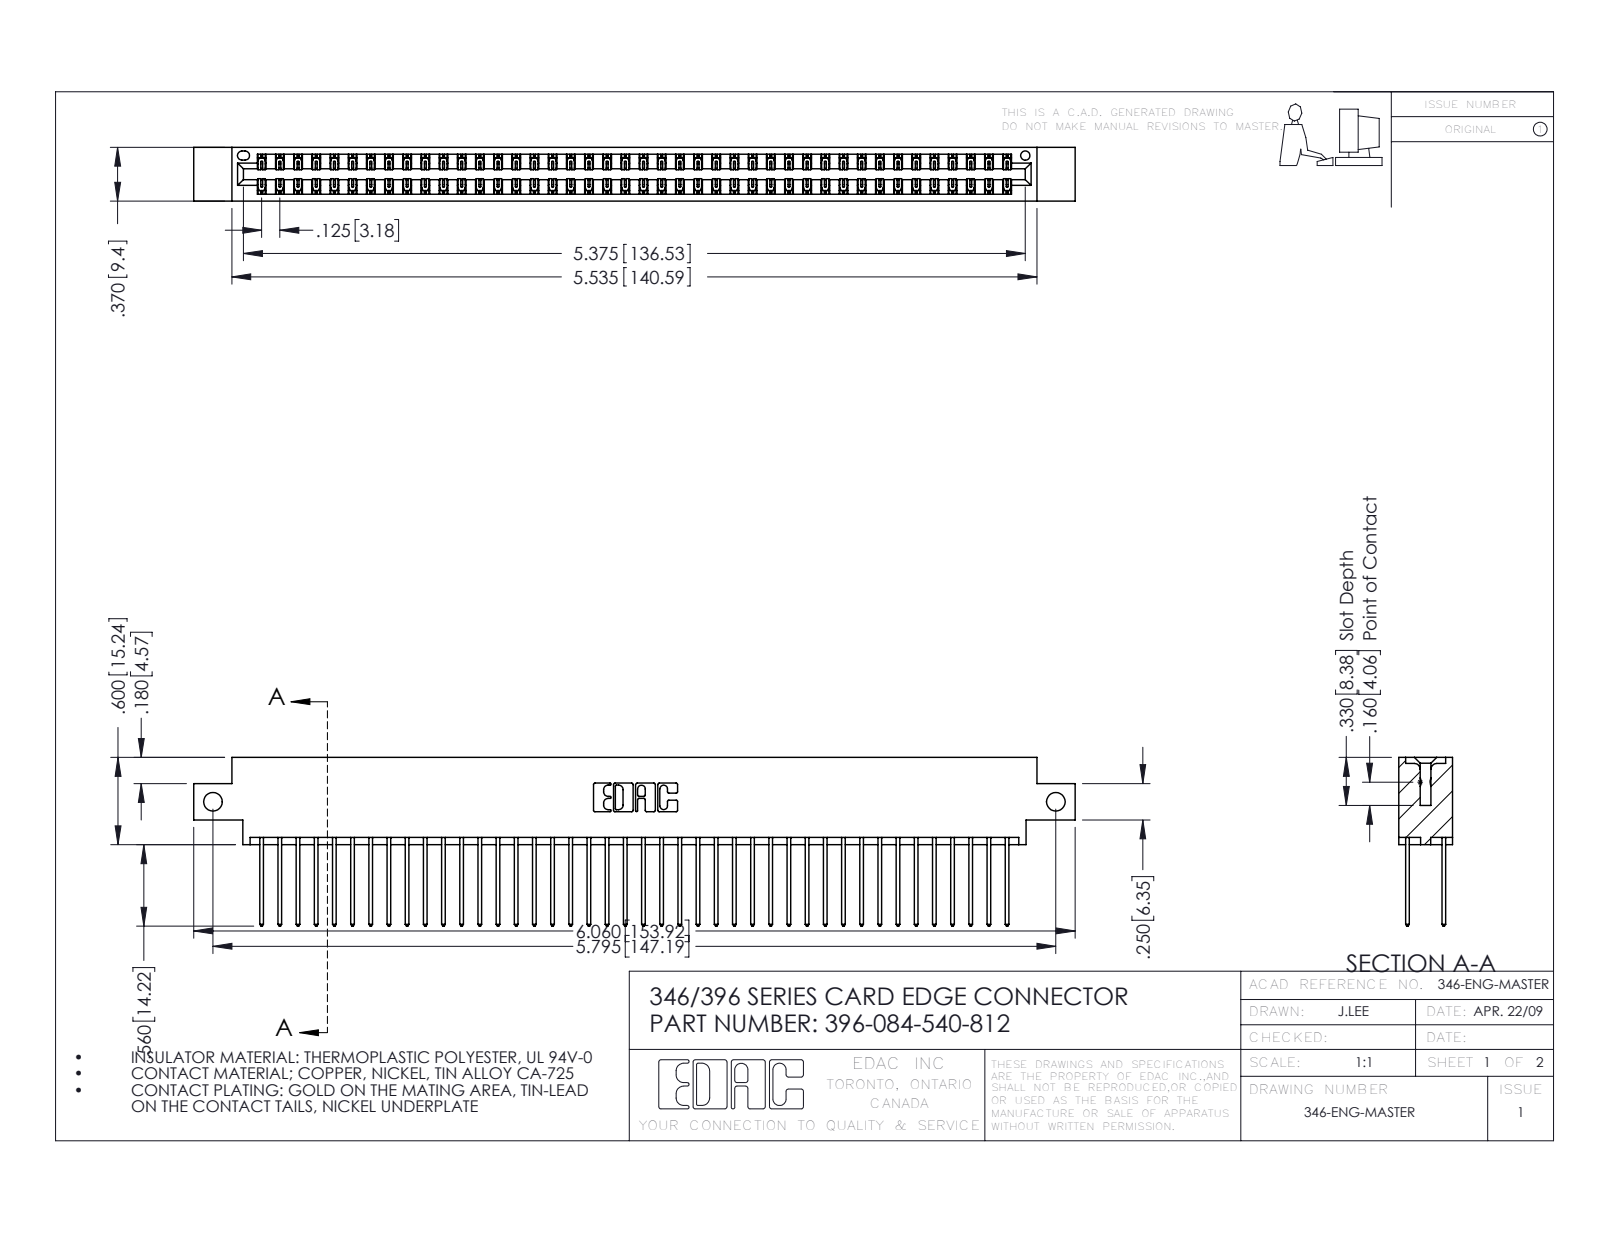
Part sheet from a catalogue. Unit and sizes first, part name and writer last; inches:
Units: inches
Overall size (bounding box): 6.06 × 1.16 × 0.37
Round holes (diameter × count): ⌀0.128 ×2, ⌀0.064 ×1
Partial cylindrical surfaces — rounded edges, fillets, slot ends (radius × count): R0.006 ×126, R0.01 ×84, R0.01 ×22, R0.007 ×6, R0.031 ×6, R0.026 ×3, R0.014 ×2, R0.022 ×2
Main face-to-face distances: 0.048, 0.322, 0.25, 0.072, 0.298, 0.025, 0.37, 0.275, 0.148, 0.222
Hole centre spacings: 5.795
Volume: 0.921 in³ · Surface area: 34.54 in²
Bodies: 85 solids, 4494 faces (3020 planar, 1474 cylindrical, 0 other)
Part name (STEP PRODUCT): 345-292-001_345-293-140; 396-084-540-812; 346 Part_0.170 Offset - Side Mount
STEP written by: SolidWorks 2016 (CONFIG_CONTROL_DESIGN)
